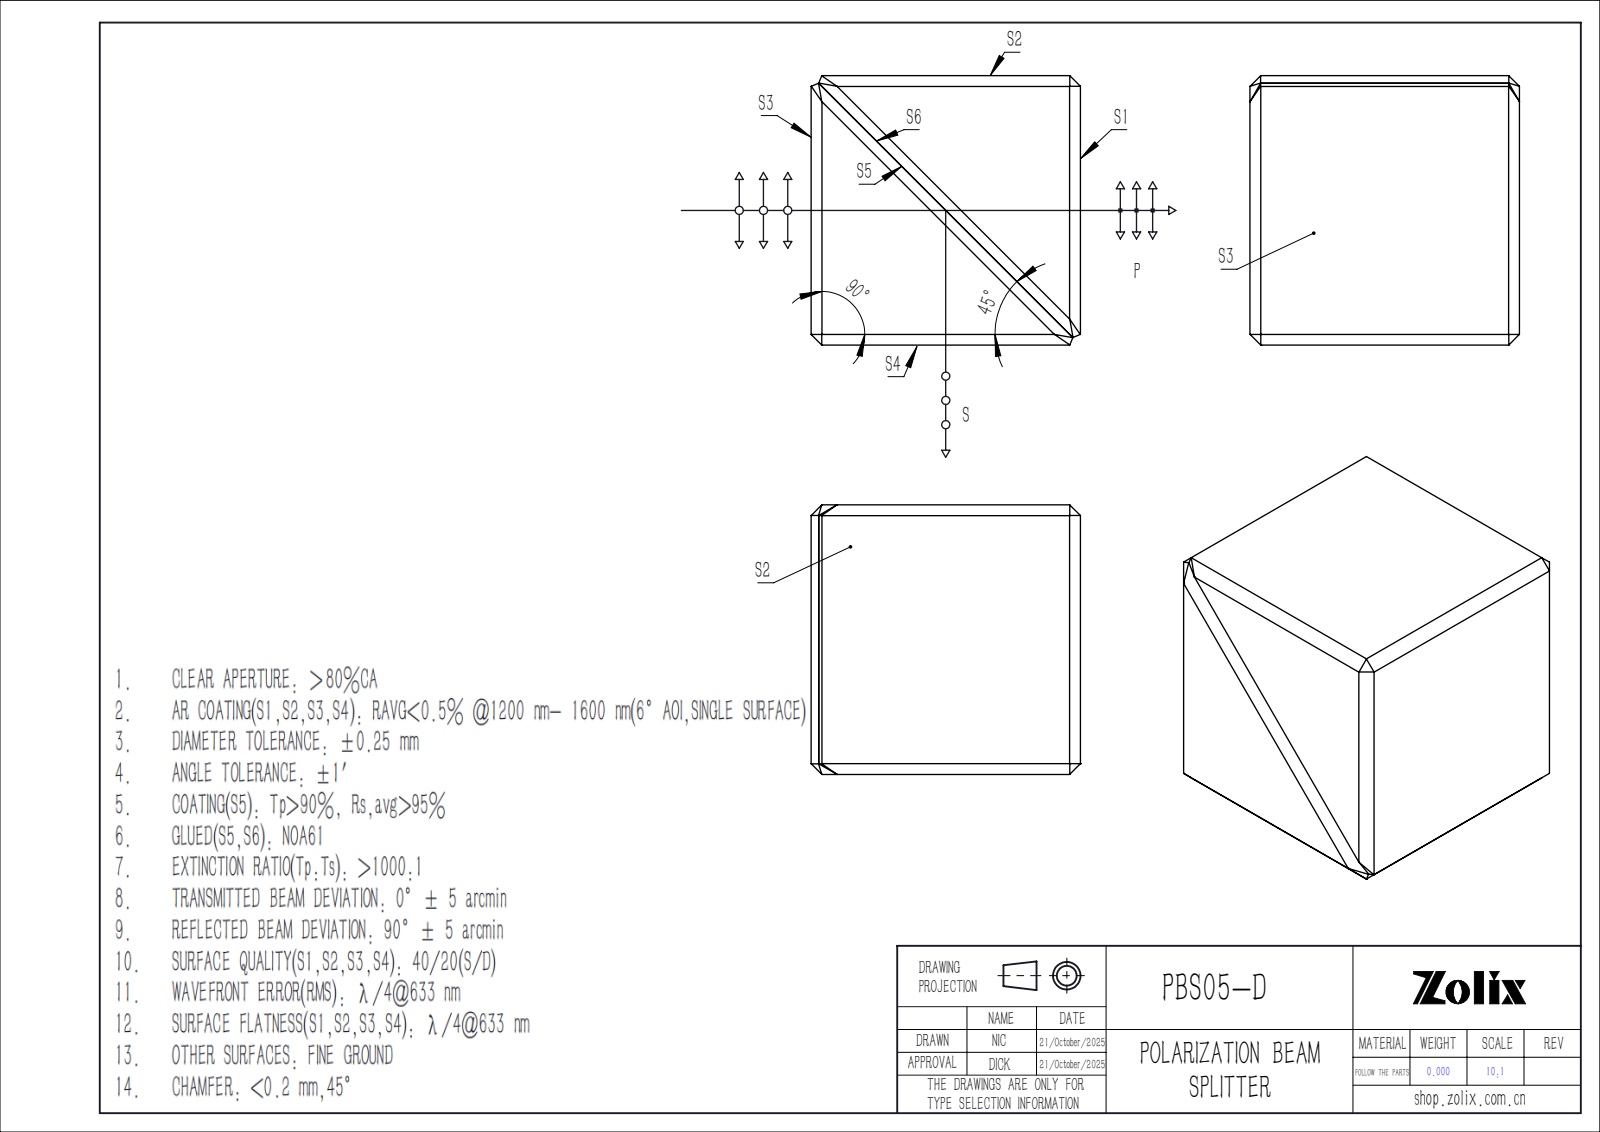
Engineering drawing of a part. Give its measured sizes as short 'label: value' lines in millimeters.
name: PBS604-1-1; PBS604-1-2; PBS604
written by: SolidWorks 2022 (CONFIG_CONTROL_DESIGN)
unit: mm
bodies: 2 solids, 43 faces (41 planar, 2 cylindrical, 0 other)
size: 5 × 5 × 5
volume: 123 mm³; area: 206 mm²
holes: 1× ⌀0.2
face distances: 5, 6.79, 3.25, 3.39, 6.78, 6.16, 6.17, 7.08, 8.19, 8.2
